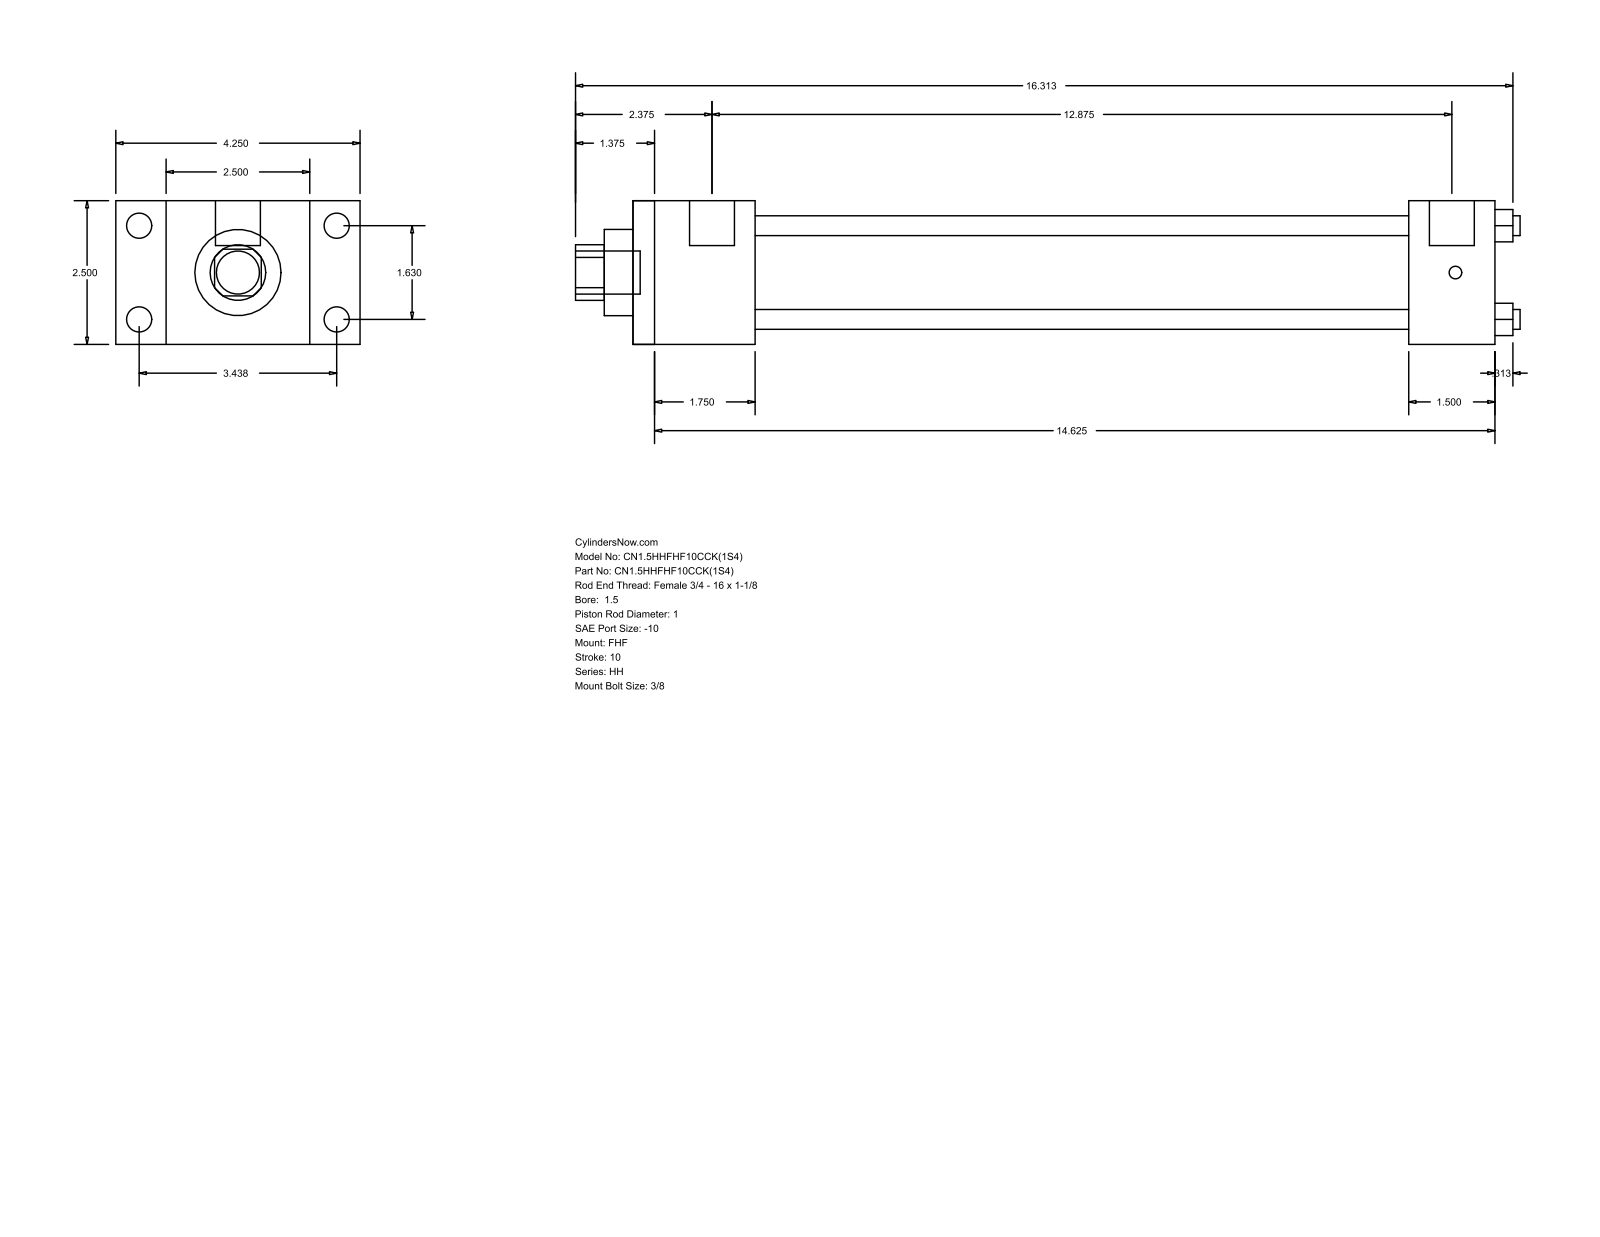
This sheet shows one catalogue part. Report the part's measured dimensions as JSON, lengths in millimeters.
{"part_name": "HH_FHF__0150_1", "step_written_by": "GSSL Pune (CONFIG_CONTROL_DESIGN)", "units": "millimeters", "bodies": {"solids": 0, "faces": 88, "planar": 60, "cylindrical": 28, "other": 0}, "overall_size": [417.51, 107.95, 63.5], "round_holes": [[8.76, 4], [25.4, 1], [38.1, 1], [44.45, 1]], "round_bosses_or_shafts": [[11.13, 4], [5.56, 4], [19.84, 2], [19.05, 1]], "partial_cylinders_radius": [[12.29, 1]], "face_to_face_distances": [63.5, 22.23, 85.73, 53.98, 107.96, 381, 327.02, 342.9, 288.92, 38.1], "hole_center_spacings": [29.27, 41.4, 58.55]}
